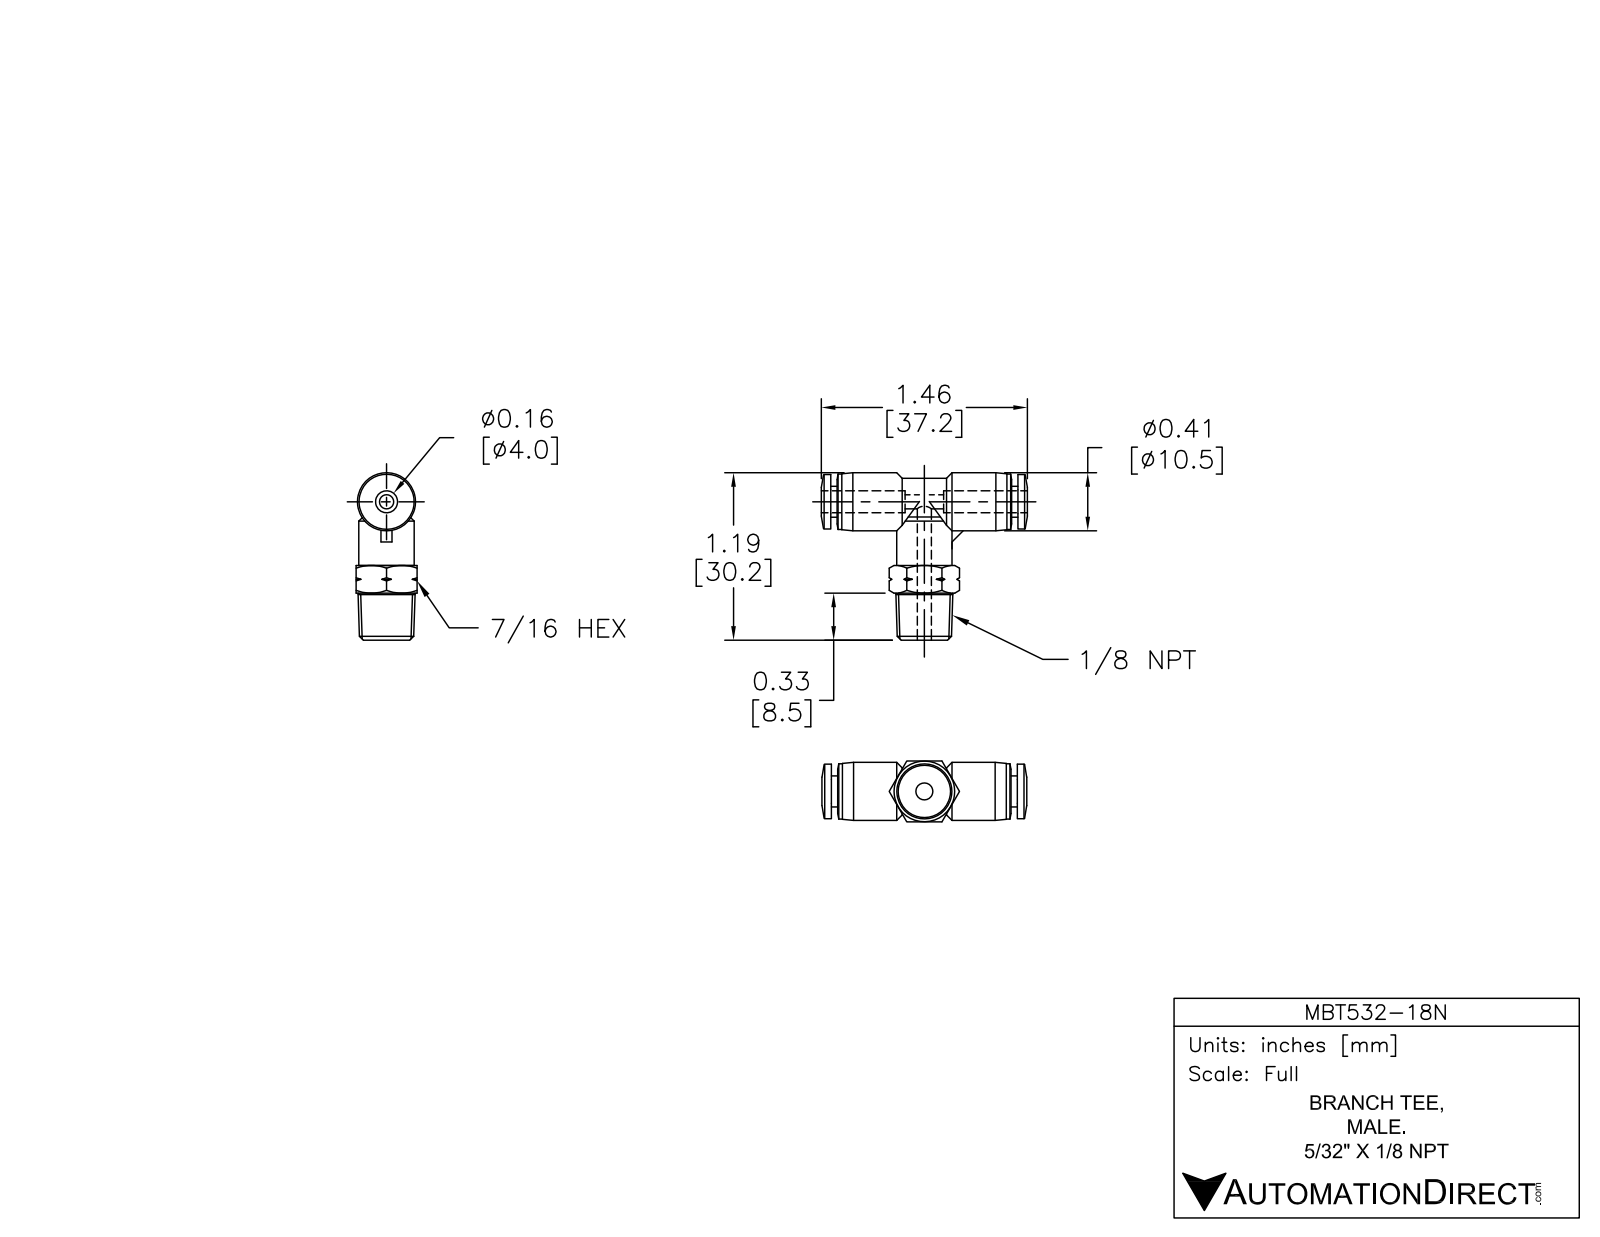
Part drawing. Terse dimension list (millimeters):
name: MBT532-18N
written by: SolidWorks 2015 (AUTOMOTIVE_DESIGN)
unit: mm
bodies: 1 solid, 114 faces (23 planar, 30 cylindrical, 61 other)
size: 37 × 30.3 × 11
volume: 3 800 mm³; area: 2 890 mm²
holes: 2× ⌀3, 1× ⌀4.3
bosses: 2× ⌀10, 1× ⌀10.5, 1× ⌀9.9, 1× ⌀8, 1× ⌀5.6
rounds: 1× R4
face distances: 11, 33.6, 1.1, 32.5, 31.3, 13.5, 13.1, 20.5, 11.9, 19.4
